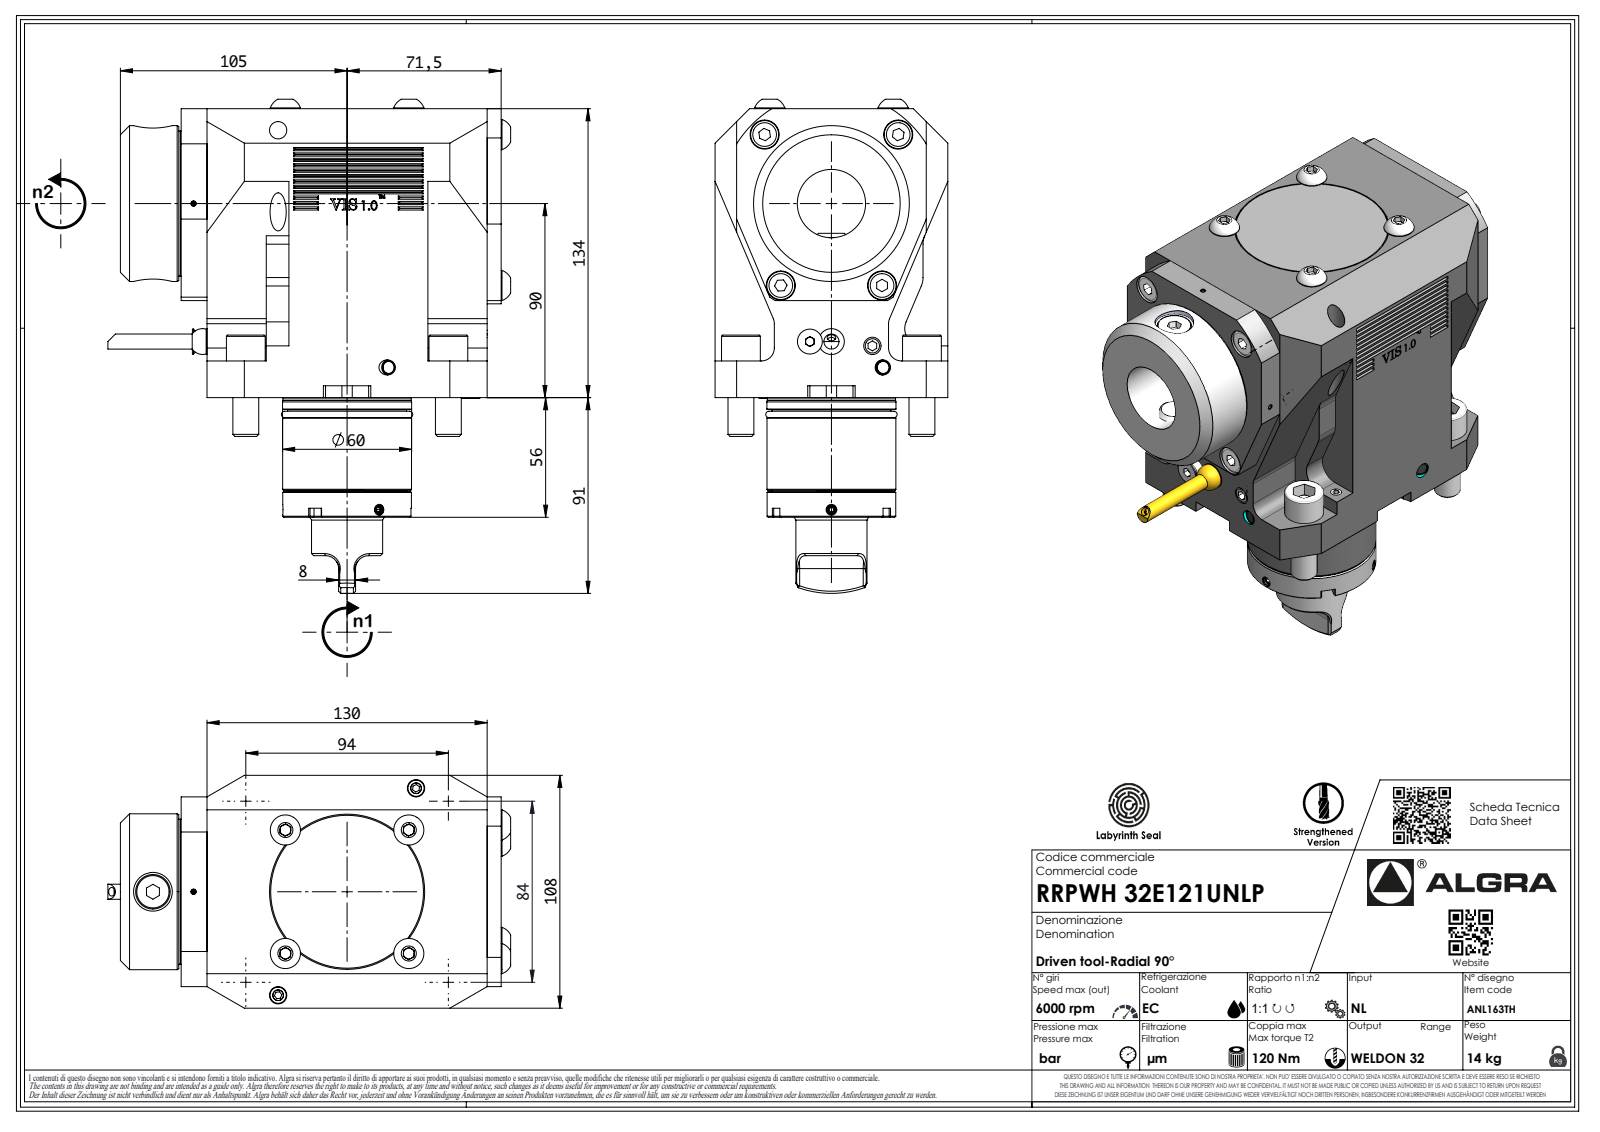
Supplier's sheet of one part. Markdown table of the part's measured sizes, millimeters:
| quantity | value |
| --- | --- |
| part name | RRPWH32E121UNLP |
| STEP written by | SolidWorks 2023 (AUTOMOTIVE_DESIGN) |
| units | millimeters |
| bodies | 1 solid, 935 faces (640 planar, 117 cylindrical, 178 other) |
| overall size | 224.8 × 182.5 × 108 |
| volume | 2 039 000 mm³ |
| surface area | 129 420 mm² |
| round holes (diameter × count) | 2.1 × 1, 4 × 1, 14 × 1, 18 × 1, 25.1 × 1 |
| round bosses / shafts (diameter × count) | 18 × 4, 12 × 4, 65.3 × 1, 59.9 × 1, 59.8 × 1, 59.7 × 1, 59.5 × 1, 55.2 × 1 |
| partial cylindrical surfaces (radius × count) | 0.2 × 21, 8 × 18, 6 × 10, 0.33 × 7, 0.52 × 7, 3.7 × 7, 10 × 4, 3 × 3 |
| main face-to-face distances | 134, 108, 27.5, 12, 148.5, 102.5, 6.5, 136.5, 5.5, 39.5 |
